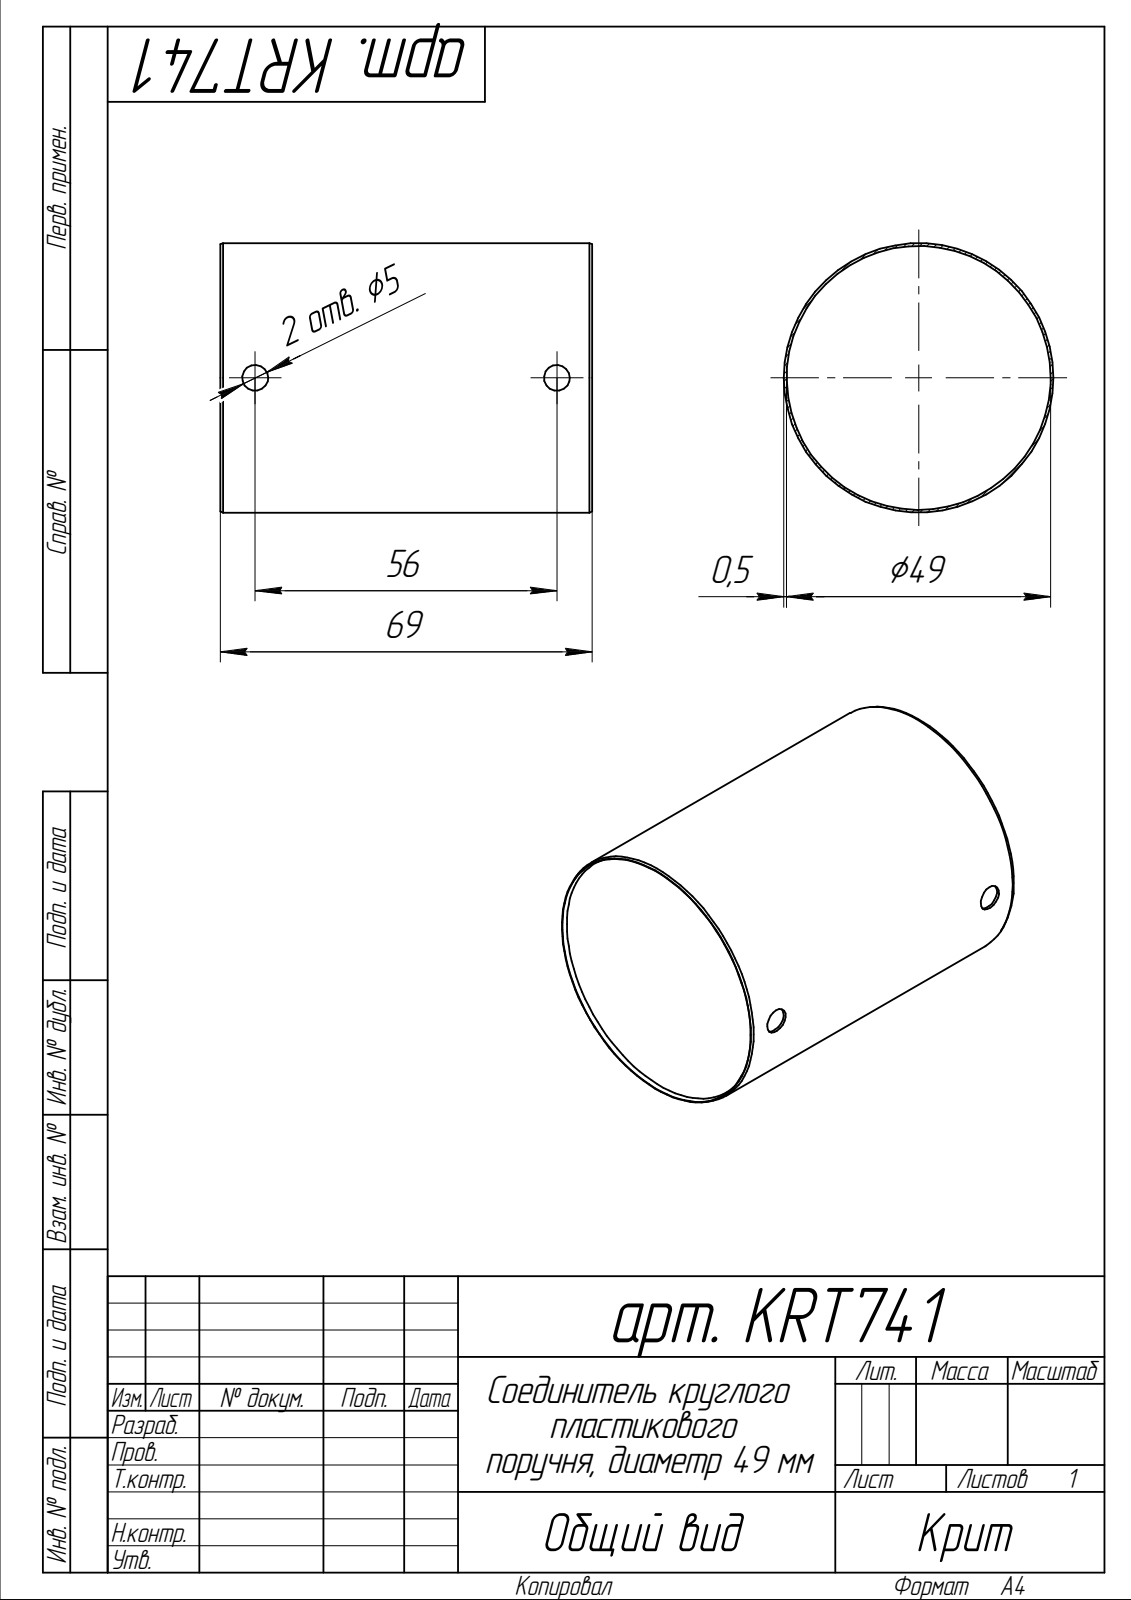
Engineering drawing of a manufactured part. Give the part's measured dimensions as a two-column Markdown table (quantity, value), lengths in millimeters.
| quantity | value |
| --- | --- |
| STEP written by | SolidWorks 2014 (AUTOMOTIVE_DESIGN) |
| units | millimeters |
| bodies | 1 solid, 18 faces (2 planar, 8 cylindrical, 8 other) |
| overall size | 69 × 50 × 50 |
| volume | 5 300 mm³ |
| surface area | 21 453 mm² |
| round holes (diameter × count) | 4.8 × 2, 49 × 1 |
| round bosses / shafts (diameter × count) | 50 × 1 |
| main face-to-face distances | 69 |
| hole center spacings | 56 |
